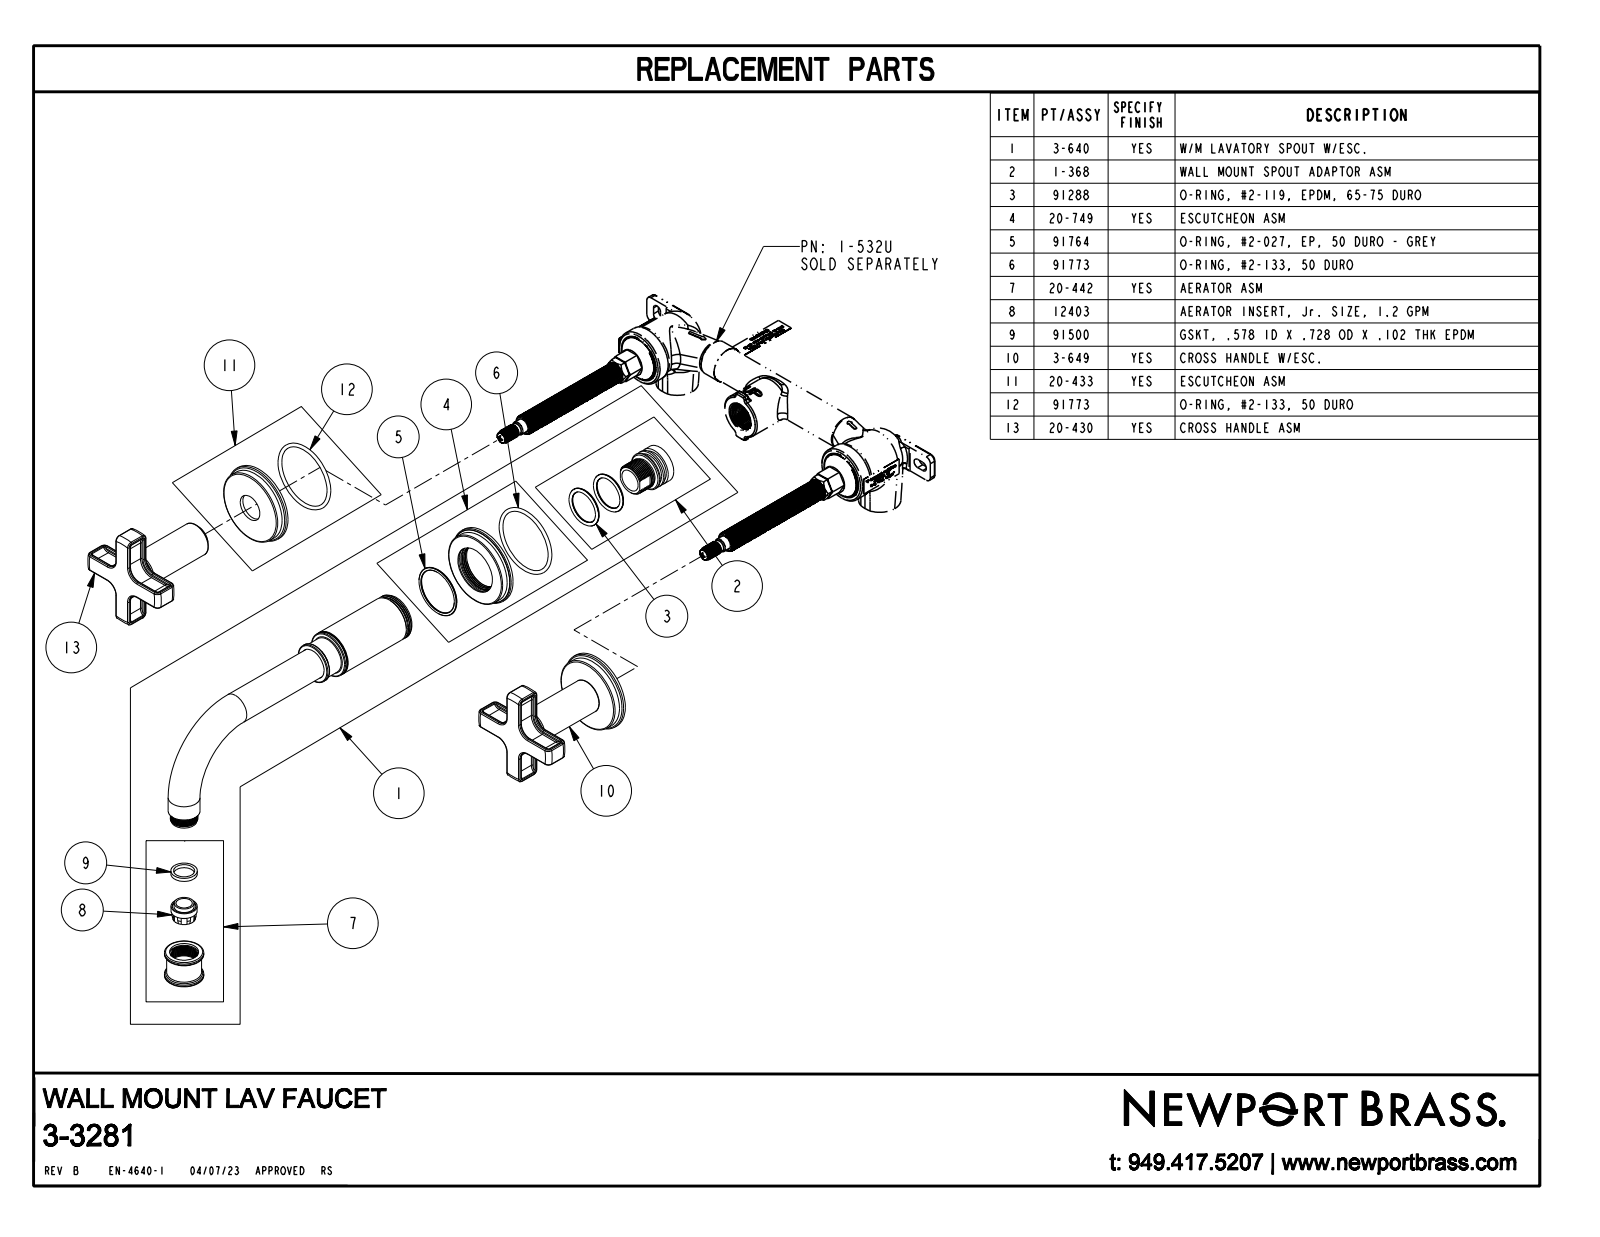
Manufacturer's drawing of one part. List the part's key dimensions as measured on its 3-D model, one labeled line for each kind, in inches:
Part name (STEP PRODUCT): 3-3281_SW0001
STEP written by: CREO PARAMETRIC BY PTC INC, 2018400 (AUTOMOTIVE_DESIGN)
Units: inches
Bodies: 3 solids, 505 faces (67 planar, 218 cylindrical, 220 other)
Overall size (bounding box): 10.674 × 8.79 × 4.66
Volume: 18.13 in³ · Surface area: 103.4 in²
Round bosses / shafts (diameter × count): ⌀2.25 ×3, ⌀2.09 ×3, ⌀0.975 ×2, ⌀0.875 ×2, ⌀0.85 ×2, ⌀0.506 ×2, ⌀1.312 ×1, ⌀1.14 ×1
Partial cylindrical surfaces — rounded edges, fillets, slot ends (radius × count): R0.03 ×68, R0.25 ×16, R0.325 ×8, R0.425 ×8, R1.4 ×2
Main face-to-face distances: 0.35, 3.251, 2.901, 2.551, 2.201, 0.7, 0.1, 0.3, 0.6, 0.4
